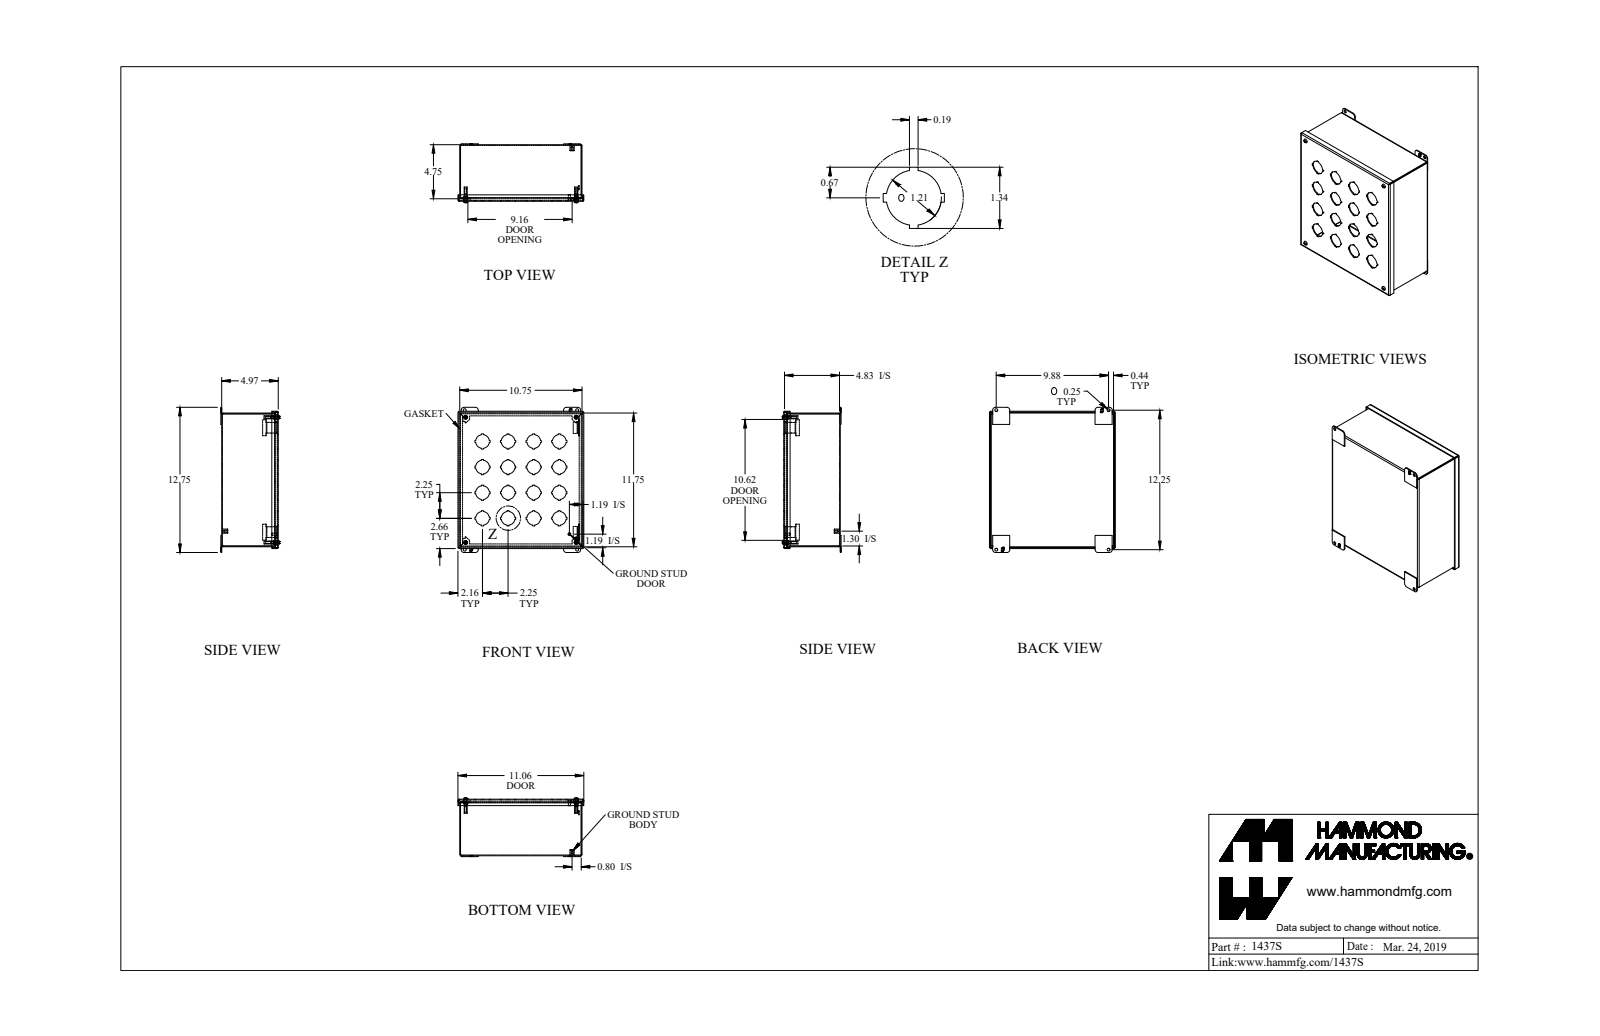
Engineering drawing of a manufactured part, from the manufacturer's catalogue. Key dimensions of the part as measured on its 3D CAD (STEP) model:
Part name (STEP PRODUCT): 1437S_Default
STEP written by: SolidWorks 2019 (CONFIG_CONTROL_DESIGN)
Units: inches
Bodies: 23 solids, 971 faces (691 planar, 224 cylindrical, 56 other)
Overall size (bounding box): 12.75 × 11.062 × 5.171
Volume: 39.62 in³ · Surface area: 1 062 in²
Round holes (diameter × count): ⌀1.21 ×16, ⌀0.25 ×8, ⌀0.159 ×4, ⌀0.406 ×4, ⌀0.156 ×1
Round bosses / shafts (diameter × count): ⌀0.39 ×4, ⌀0.275 ×4, ⌀0.19 ×4, ⌀0.148 ×4, ⌀0.375 ×1, ⌀0.25 ×1, ⌀0.188 ×1
Partial cylindrical surfaces — rounded edges, fillets, slot ends (radius × count): R0.036 ×12, R0.108 ×12, R0.25 ×8, R0.029 ×4, R0.086 ×4, R0.16 ×4, R0.171 ×4
Main face-to-face distances: 0.072, 4.9, 4.828, 4.972, 10.678, 0.072, 11.678, 10.606, 10.75, 11.75
Hole centre spacings: 2.25, 5.031, 3.182, 4.5, 7.115, 11, 11.626, 6.364
